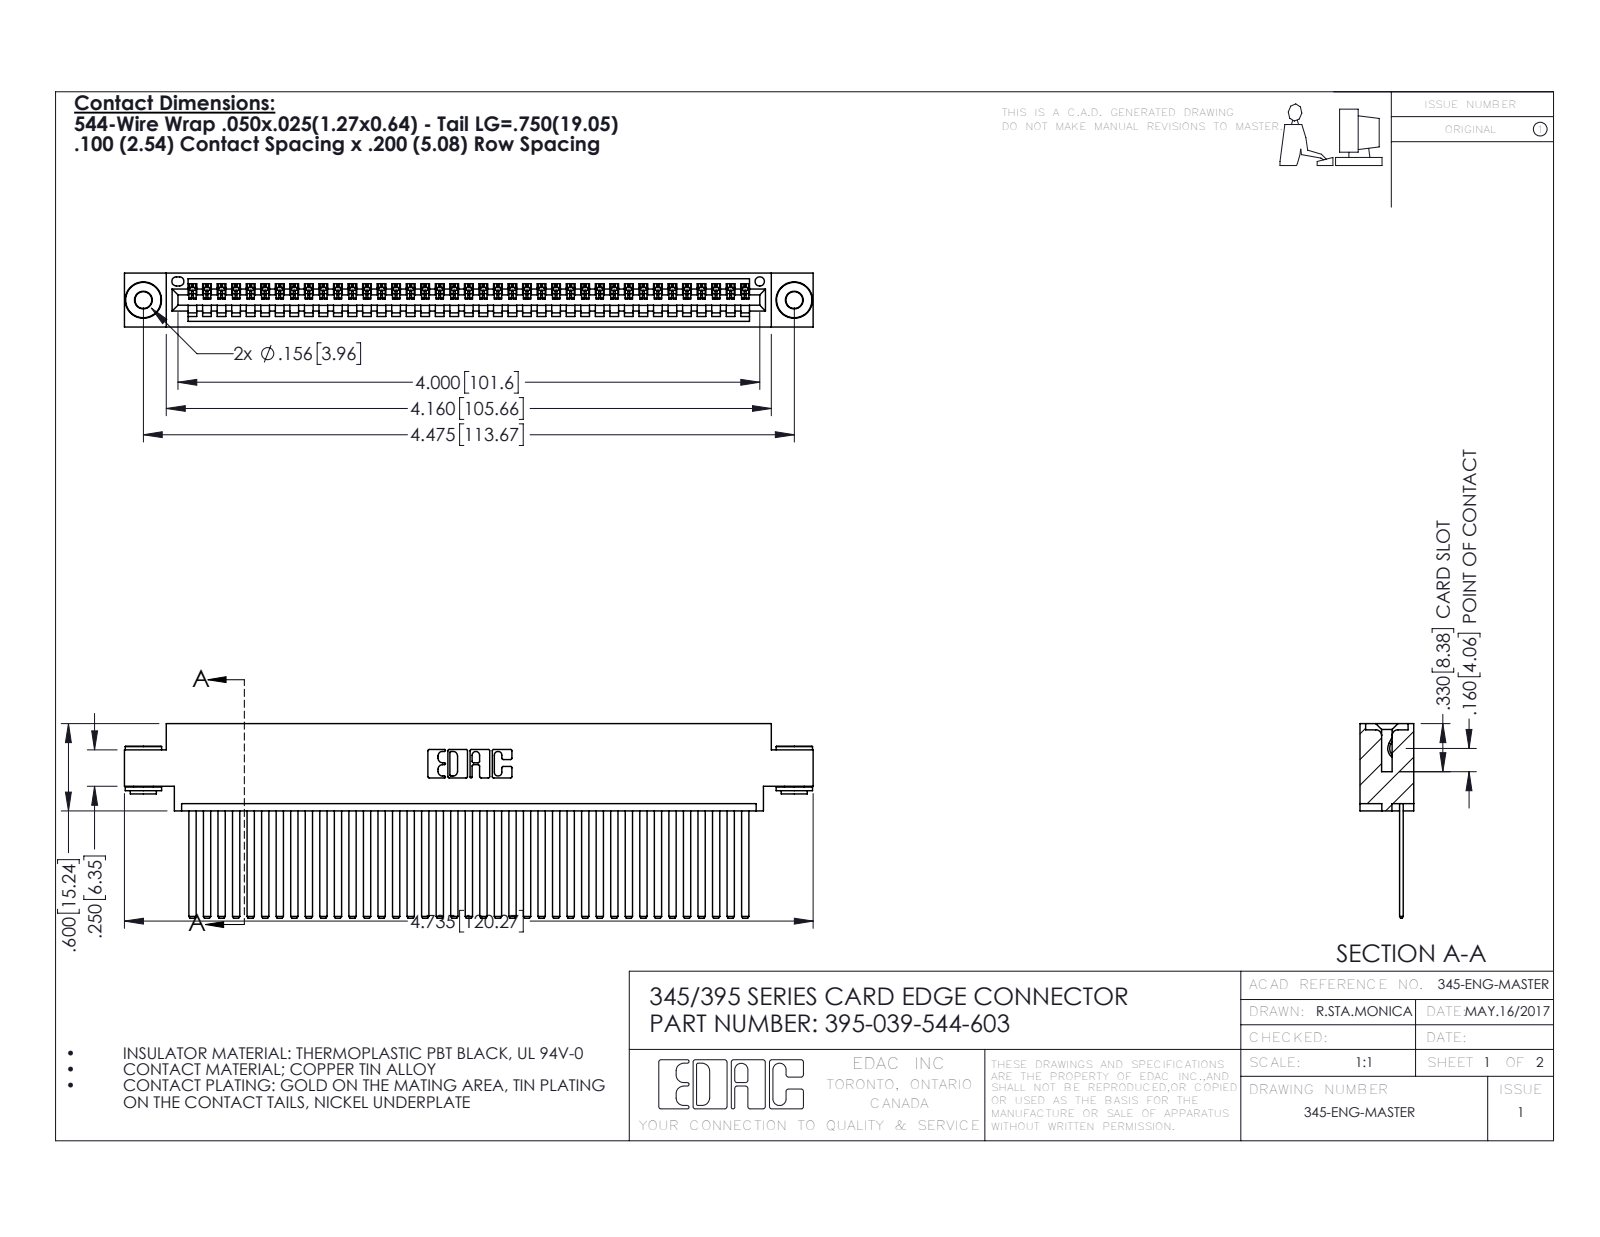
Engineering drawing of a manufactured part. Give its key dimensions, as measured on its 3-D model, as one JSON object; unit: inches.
{"part_name": "395-039-544-603; 345-250-002_345-250-002-102; 345-292-001_345-293-144; 345 Part_0.170 Offset - 0.156 Dia-TH", "step_written_by": "SolidWorks 2016 (CONFIG_CONTROL_DESIGN)", "units": "inches", "bodies": {"solids": 42, "faces": 2196, "planar": 1498, "cylindrical": 690, "other": 8}, "overall_size": [4.735, 1.337, 0.37], "volume_in3": 0.717, "surface_area_in2": 26.78, "round_holes": [[0.116, 2], [0.156, 2], [0.064, 1]], "round_bosses_or_shafts": [[0.25, 2], [0.18, 2], [0.136, 2]], "partial_cylinders_radius": [[0.006, 78], [0.01, 22], [0.007, 6], [0.031, 6], [0.026, 3], [0.031, 2], [0.04, 2], [0.014, 1]], "face_to_face_distances": [0.072, 0.298, 0.025, 0.098, 0.272, 0.37, 0.2, 0.225, 0.175, 0.149], "hole_center_spacings": [0.27, 4.239, 4.475]}
